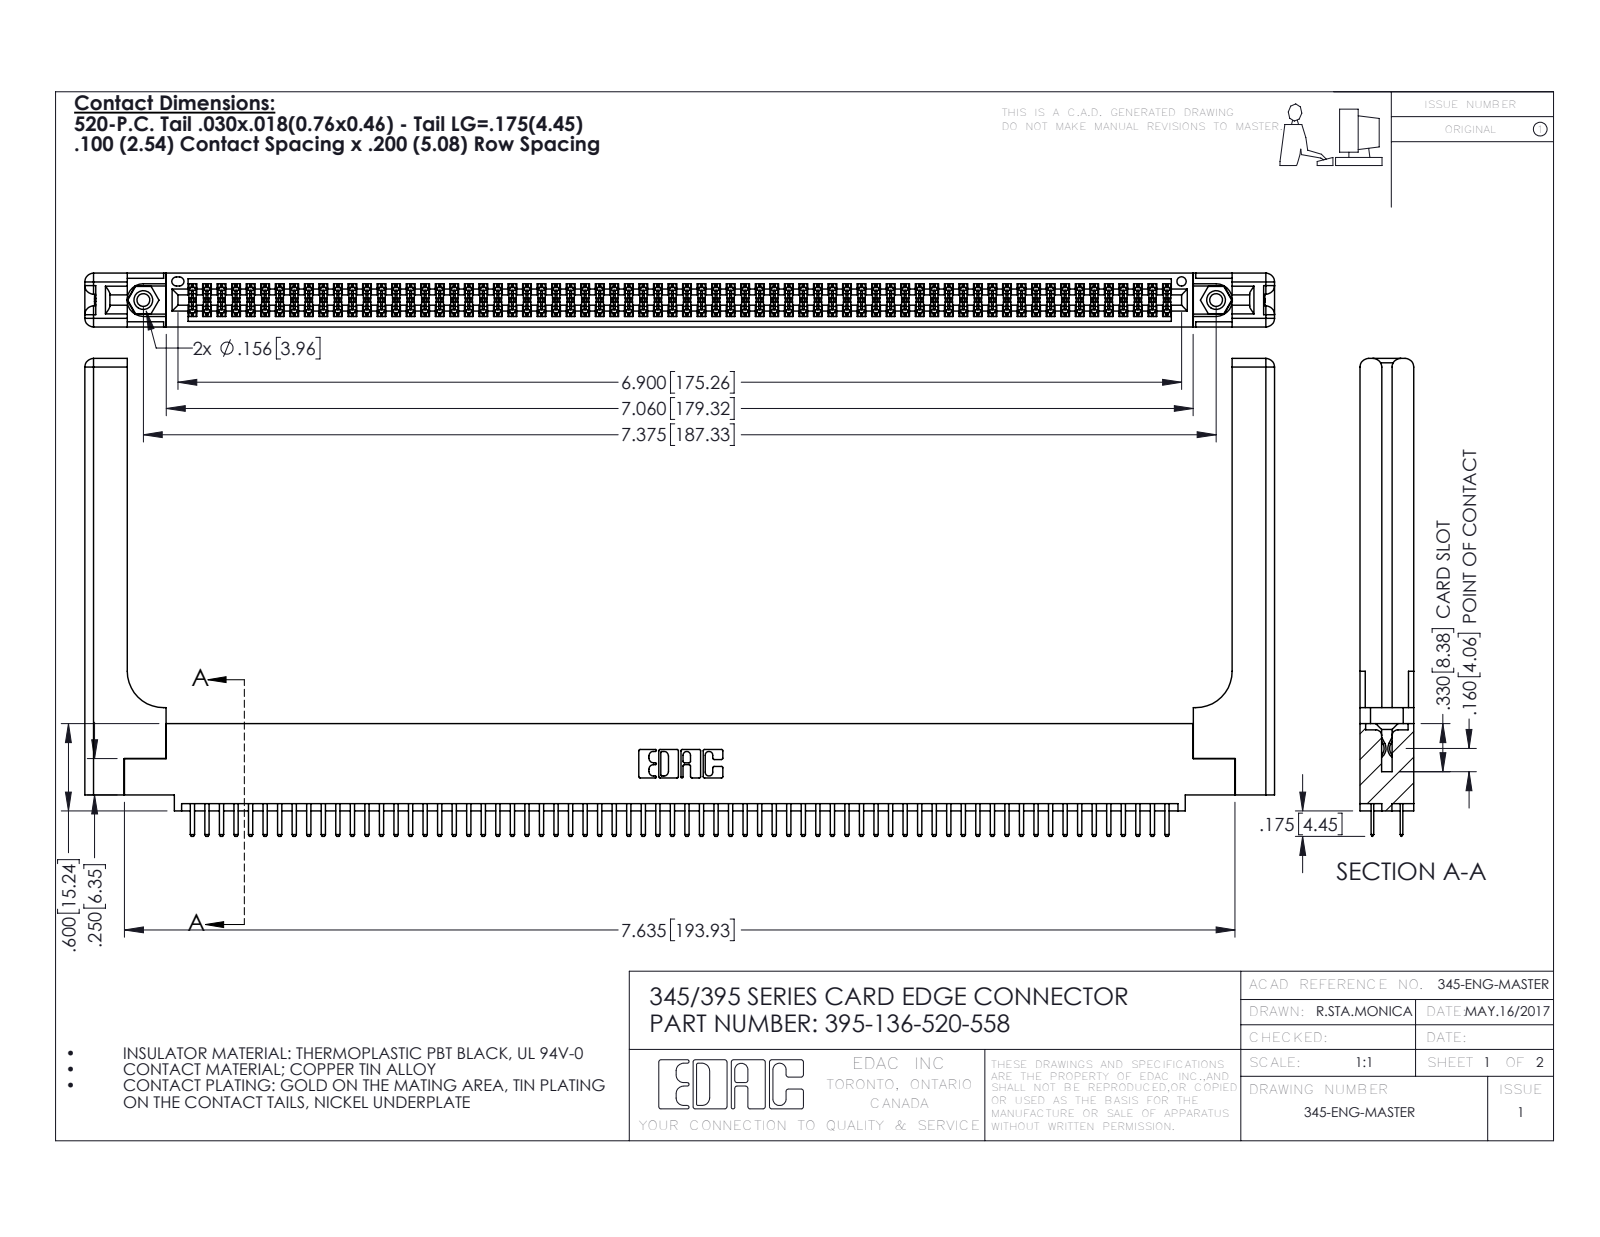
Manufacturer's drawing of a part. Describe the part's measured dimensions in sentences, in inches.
The part is named "345-220-058_345-220-058; 345-292-001_345-293-120; 395-136-520-558; 345-250-001_345-250-001-102 (+1 more)". Its 3-D file was written by "SolidWorks 2016 (CONFIG_CONTROL_DESIGN)". It is 141 solids with 7730 faces: 4992 planar, 2678 cylindrical and 60 other. Overall it measures 8.179 by 3.285 by 0.37 inches. Its volume is 1.755 cubic inches and its surface area 55.05 square inches. Round holes: 2 of diameter 0.089, 2 of diameter 0.125, 2 of diameter 0.156, 1 of diameter 0.064. Round bosses or shafts: 2 of diameter 0.155. Partial cylindrical surfaces (rounded edges, fillets, slot ends): 204 of radius 0.006, 140 of radius 0.01, 22 of radius 0.01, 16 of radius 0.06, 6 of radius 0.007, 6 of radius 0.031, 3 of radius 0.026, 2 of radius 0.014. The main face-to-face distances are 0.072, 0.298, 0.37, 0.2, 0.098, 0.272, 0.025, 0.225, 0.022, 0.072. The hole center spacings are 0.27, 7.139, 7.375.
